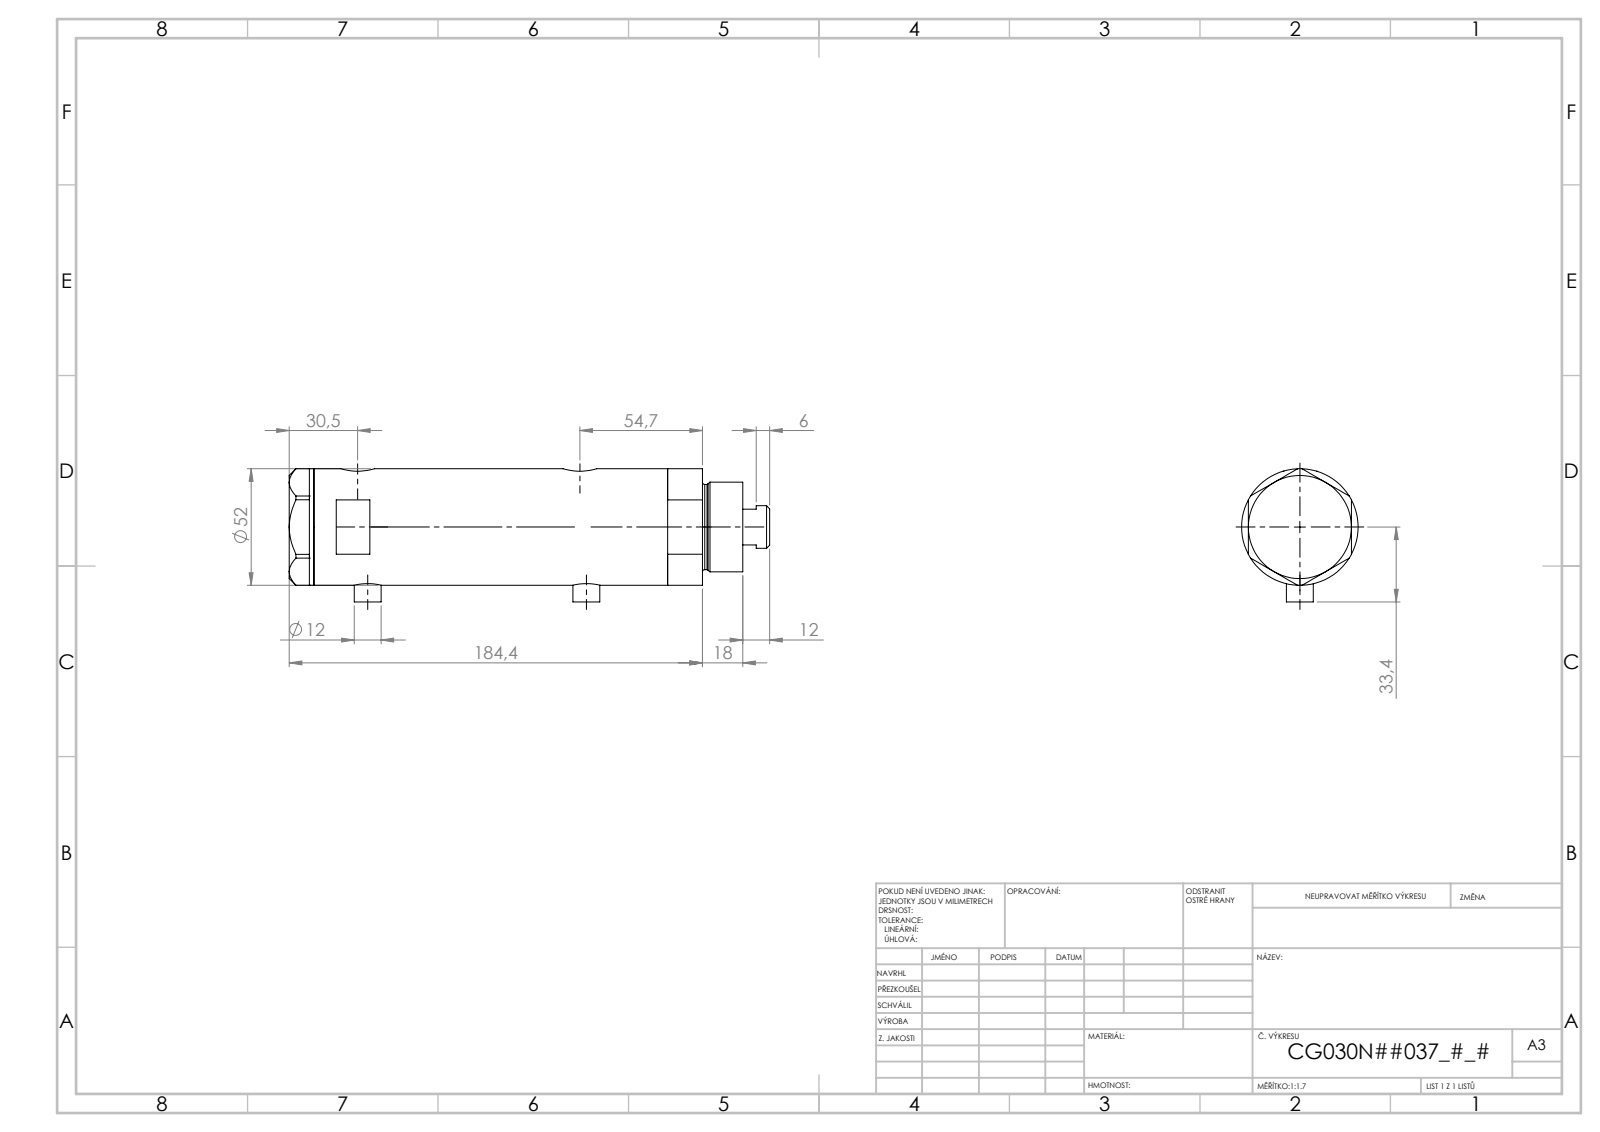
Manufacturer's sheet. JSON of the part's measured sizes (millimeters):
{"part_name": "V270CG_BACK; V270CG_VC; V270CG_MIDDLE; V270CG_FRONT", "step_written_by": "SolidWorks 2019 (CONFIG_CONTROL_DESIGN)", "units": "millimeters", "bodies": {"solids": 4, "faces": 140, "planar": 67, "cylindrical": 53, "other": 20}, "overall_size": [186.02, 53.1, 52], "volume_mm3": 331566, "surface_area_mm2": 76946, "round_holes": [[5, 2], [9.73, 2], [12.5, 2], [15, 2], [6.5, 1], [20, 1], [21.5, 1], [30, 1], [33, 1], [44, 1]], "round_bosses_or_shafts": [[12, 2], [52, 1], [40, 1], [38, 1], [19, 1]], "face_to_face_distances": [90.56, 23.8, 66.76, 11, 34.8, 101.56, 46, 137.96, 126.96, 103.16], "hole_center_spacings": [2.9, 4.5, 63.75, 66.65, 68.25, 71.15, 2.89, 2.91]}
